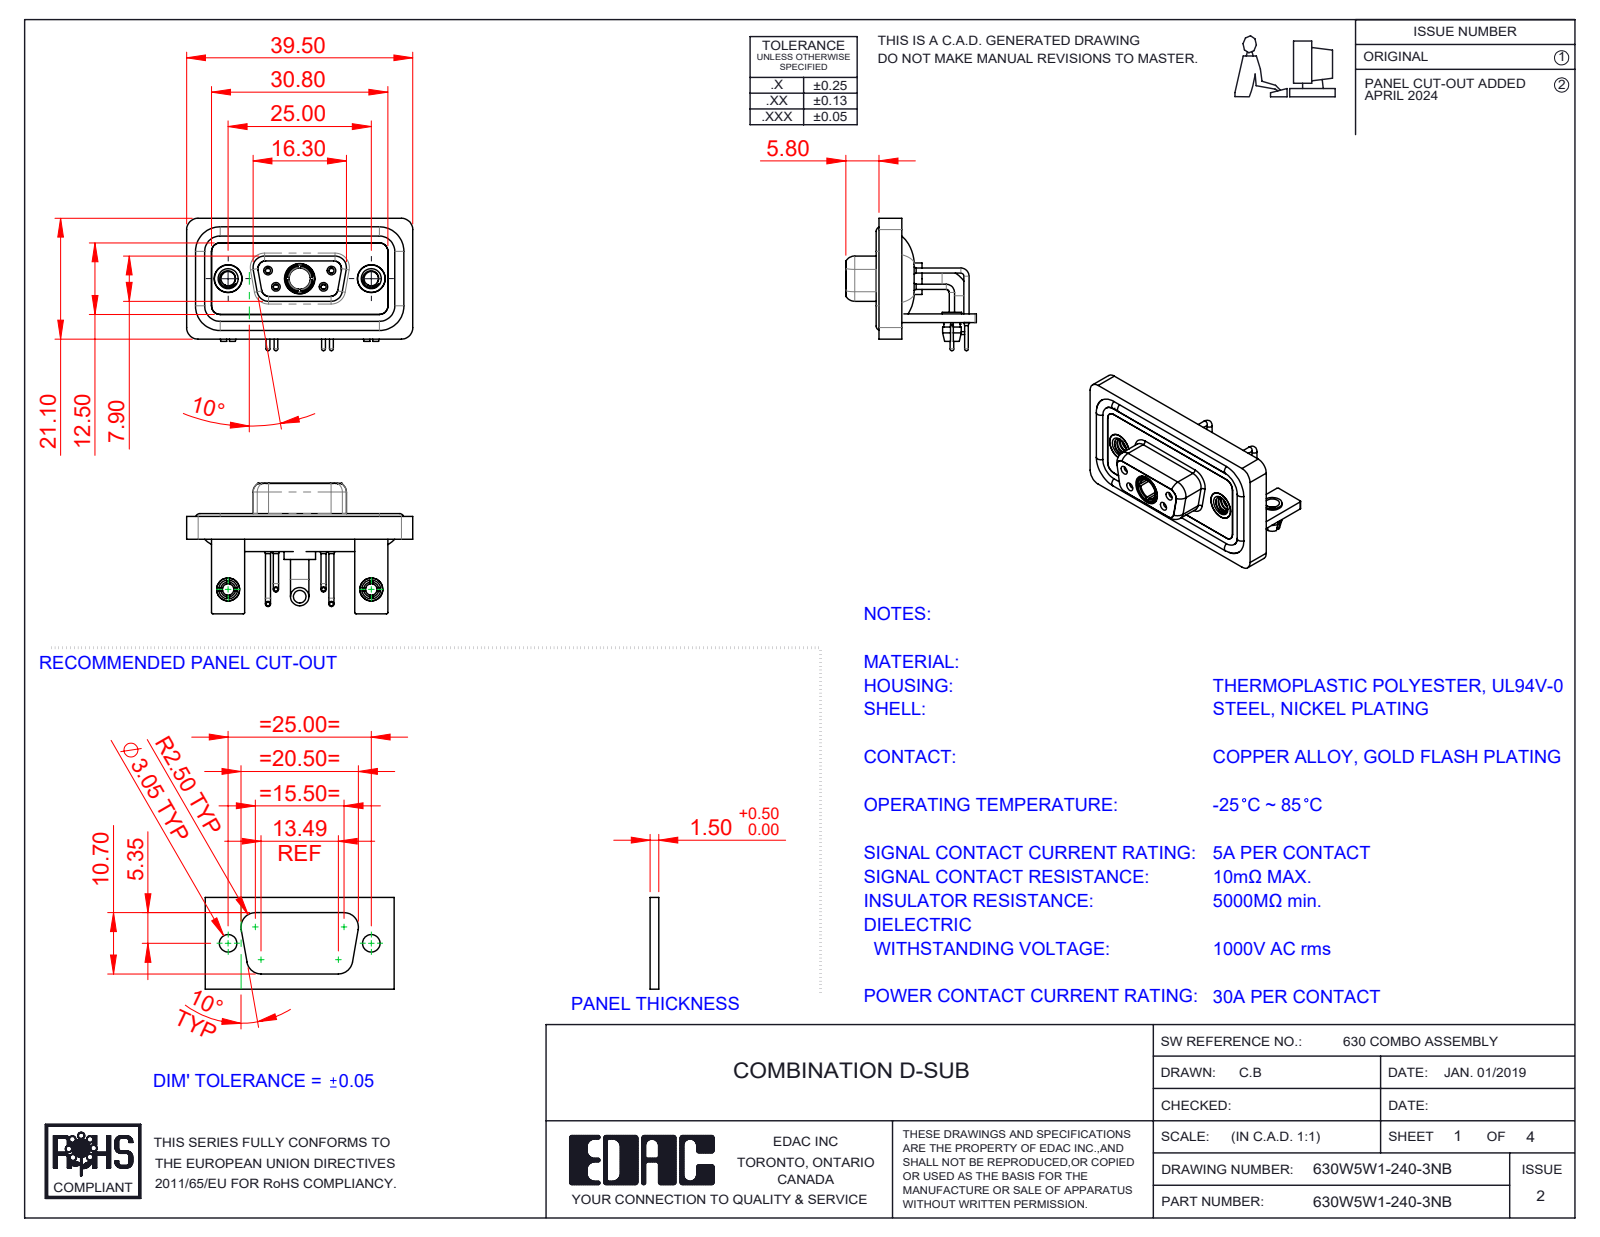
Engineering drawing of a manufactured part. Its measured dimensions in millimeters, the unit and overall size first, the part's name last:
Units: millimetres
Overall size (bounding box): 39.5 × 23.12 × 22.8
Round holes (diameter × count): ⌀2 ×6, ⌀0.9 ×4, ⌀1.1 ×4, ⌀1.5 ×4, ⌀2.5 ×4, ⌀4.85 ×3, ⌀1.6 ×2, ⌀1.7 ×2, ⌀3.2 ×2, ⌀4 ×2, ⌀4.05 ×2, ⌀5 ×2
Round bosses / shafts (diameter × count): ⌀1.6 ×6, ⌀0.9 ×4, ⌀0.65 ×4, ⌀4.95 ×2, ⌀4.8 ×2, ⌀4 ×2, ⌀3.4 ×2, ⌀3.3 ×2
Partial cylindrical surfaces — rounded edges, fillets, slot ends (radius × count): R2 ×19, R1.5 ×18, R0.25 ×16, R1.35 ×8, R1.6 ×8, R0.5 ×5, R0.6 ×4, R0.65 ×4
Main face-to-face distances: 0.4, 2.9, 1.5, 1.8, 1.1, 3.7, 1.6, 0.8, 2.5, 3.1
Hole centre spacings: 3.16, 5.72, 7.1, 12.5, 18.1, 25, 4.39, 4.4
Volume: 5 252 mm³ · Surface area: 8 811 mm²
Bodies: 17 solids, 810 faces (262 planar, 359 cylindrical, 189 other)
Part name (STEP PRODUCT): 630Combo Shell Rear_09 Contacts; 630W5W1-240-3NB; Power Socket_30A RA; 630Combo Stabilizer Bracket_50 Contacts (+7 more)
STEP written by: SolidWorks 2023 (CONFIG_CONTROL_DESIGN)
